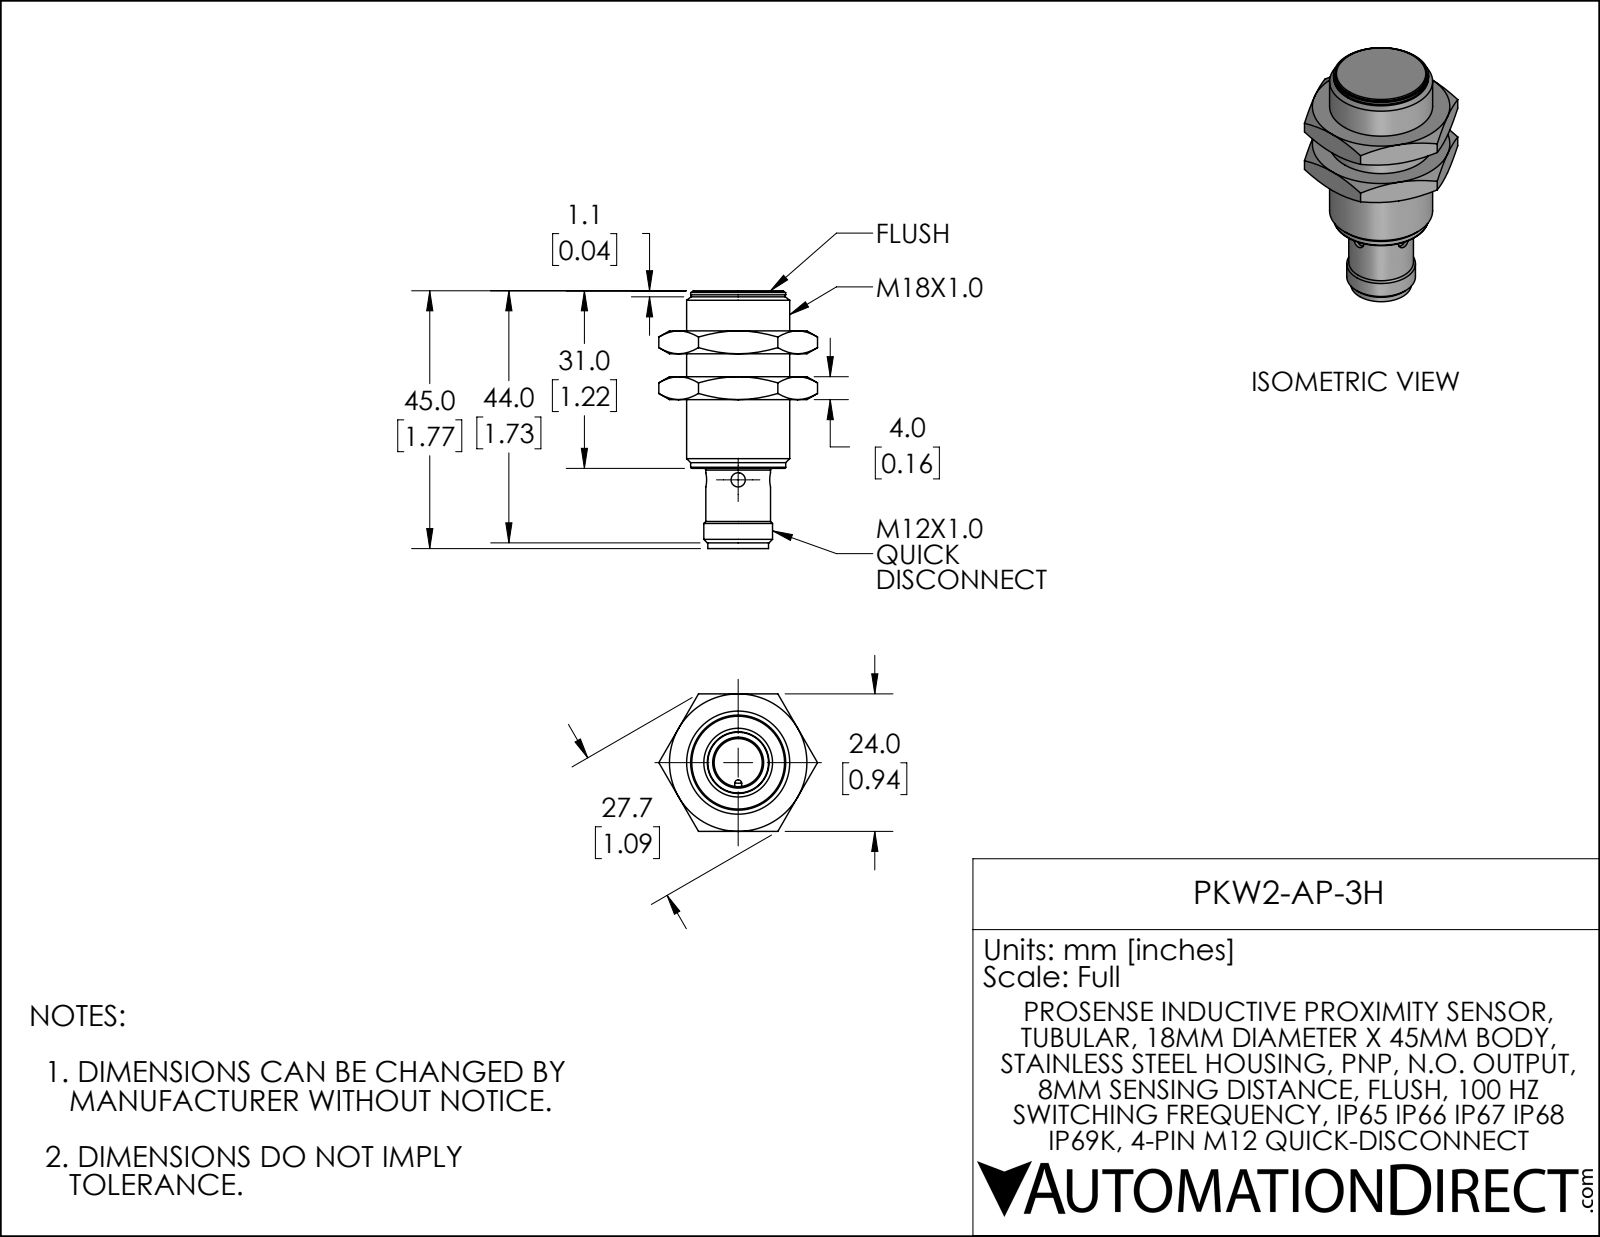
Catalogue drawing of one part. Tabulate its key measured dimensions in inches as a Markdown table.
| quantity | value |
| --- | --- |
| part name | PKW2-AP-3H |
| STEP written by | SolidWorks 2019 (CONFIG_CONTROL_DESIGN) |
| units | inches |
| bodies | 3 solids, 82 faces (25 planar, 19 cylindrical, 38 other) |
| overall size | 1.772 × 1.091 × 0.945 |
| volume | 0.661 in³ |
| surface area | 7.755 in² |
| round holes (diameter × count) | 0.098 × 2, 0.331 × 1, 0.666 × 1 |
| round bosses / shafts (diameter × count) | 0.709 × 1, 0.654 × 1, 0.63 × 1, 0.472 × 1, 0.445 × 1, 0.417 × 1 |
| partial cylindrical surfaces (radius × count) | 0.024 × 1, 0.197 × 1 |
| main face-to-face distances | 0.157, 0.945, 0.315, 0.748, 0.591, 0.433, 0.472, 0.63, 0.787, 1.22 |
